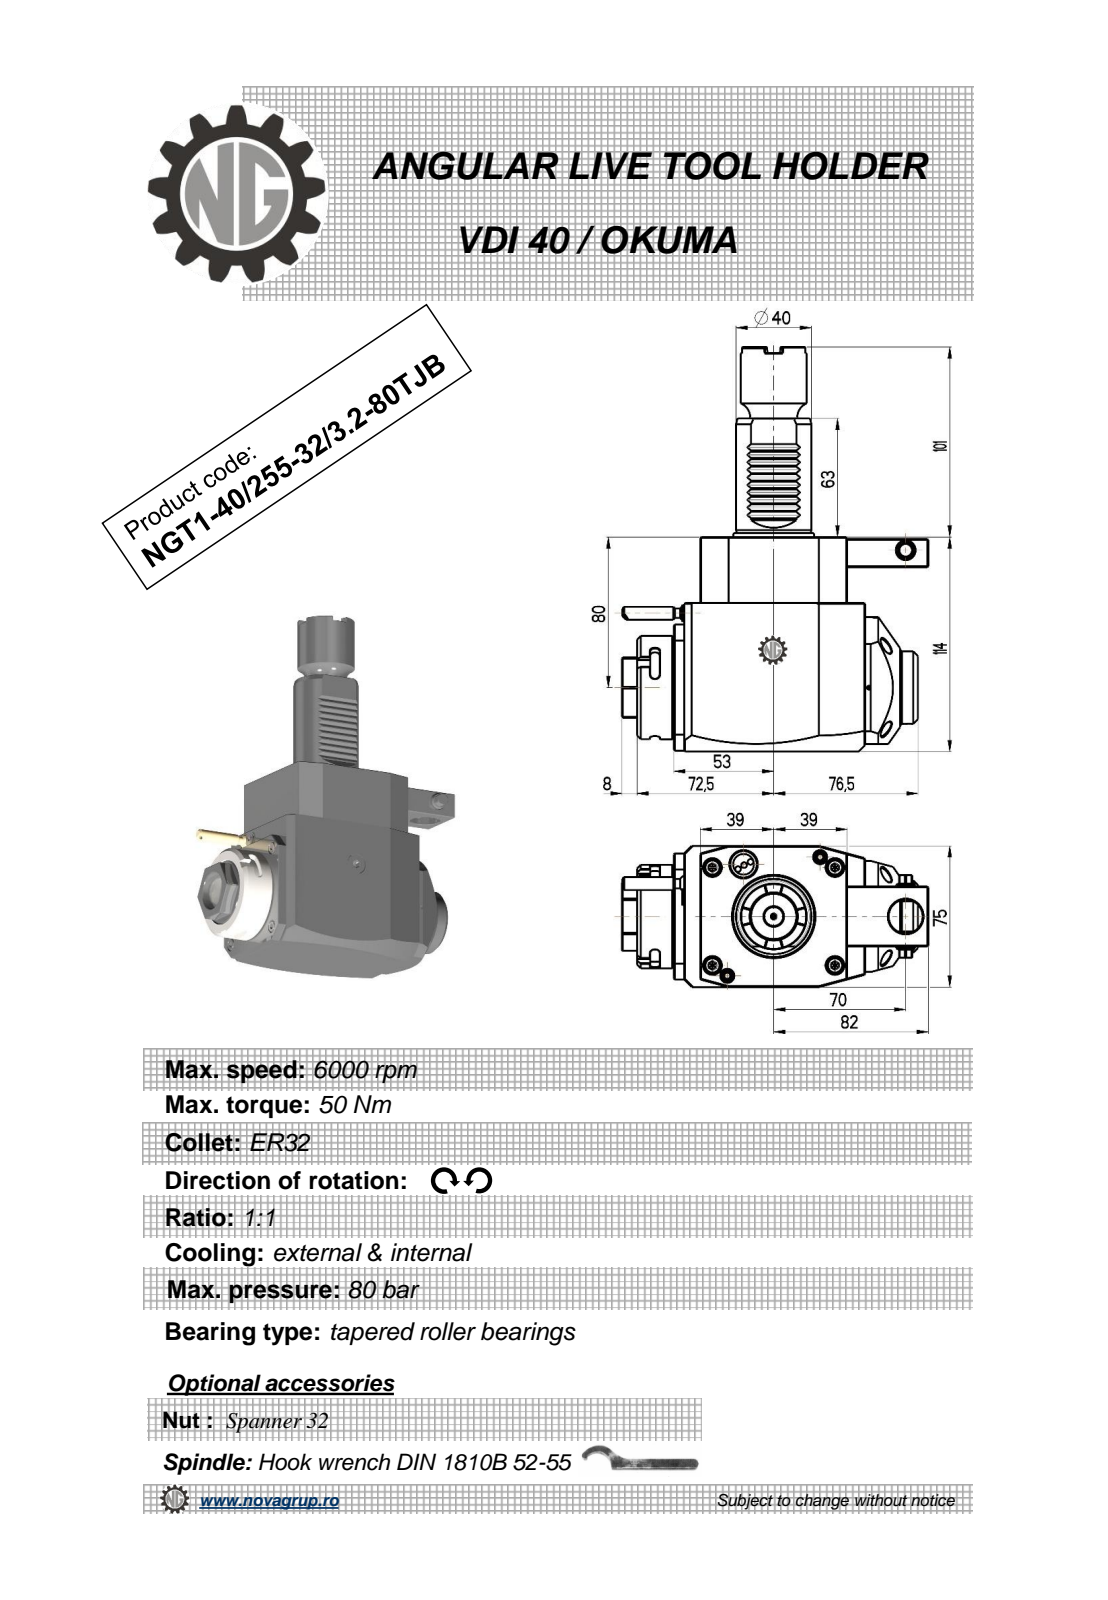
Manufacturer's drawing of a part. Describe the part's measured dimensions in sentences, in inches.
The part is named "NGT1_40_255_32_3_2_80TJB". Its 3-D file was written by "PRO/ENGINEER BY PARAMETRIC TECHNOLOGY CORPORATION, 2010280 (CONFIG_CONTROL_DESIGN)". It is 1 solid with 388 faces: 202 planar, 78 cylindrical and 108 other. Overall it measures 8.465 by 6.398 by 2.953 inches. Its volume is 61.7 cubic inches and its surface area 122.2 square inches. Round holes: 1 of diameter 0.098, 1 of diameter 0.118, 1 of diameter 0.374, 1 of diameter 0.709, 1 of diameter 0.906, 1 of diameter 0.984. Round bosses or shafts: 2 of diameter 0.353, 1 of diameter 2.165, 1 of diameter 1.89, 1 of diameter 1.575, 1 of diameter 1.516, 1 of diameter 1.378, 1 of diameter 0.394, 1 of diameter 0.276. Partial cylindrical surfaces (rounded edges, fillets, slot ends): 10 of radius 0.012, 6 of radius 0.098, 2 of radius 7.087, 1 of radius 0.02, 1 of radius 0.152, 1 of radius 0.167, 1 of radius 0.965, 1 of radius 1.476. The main face-to-face distances are 2.953, 4.488, 0.551, 1.319, 3.11, 3.622, 3.071, 0.846, 0.768, 4.39. The hole center spacings are 1.47, 1.701, 2.756, 2.854.
